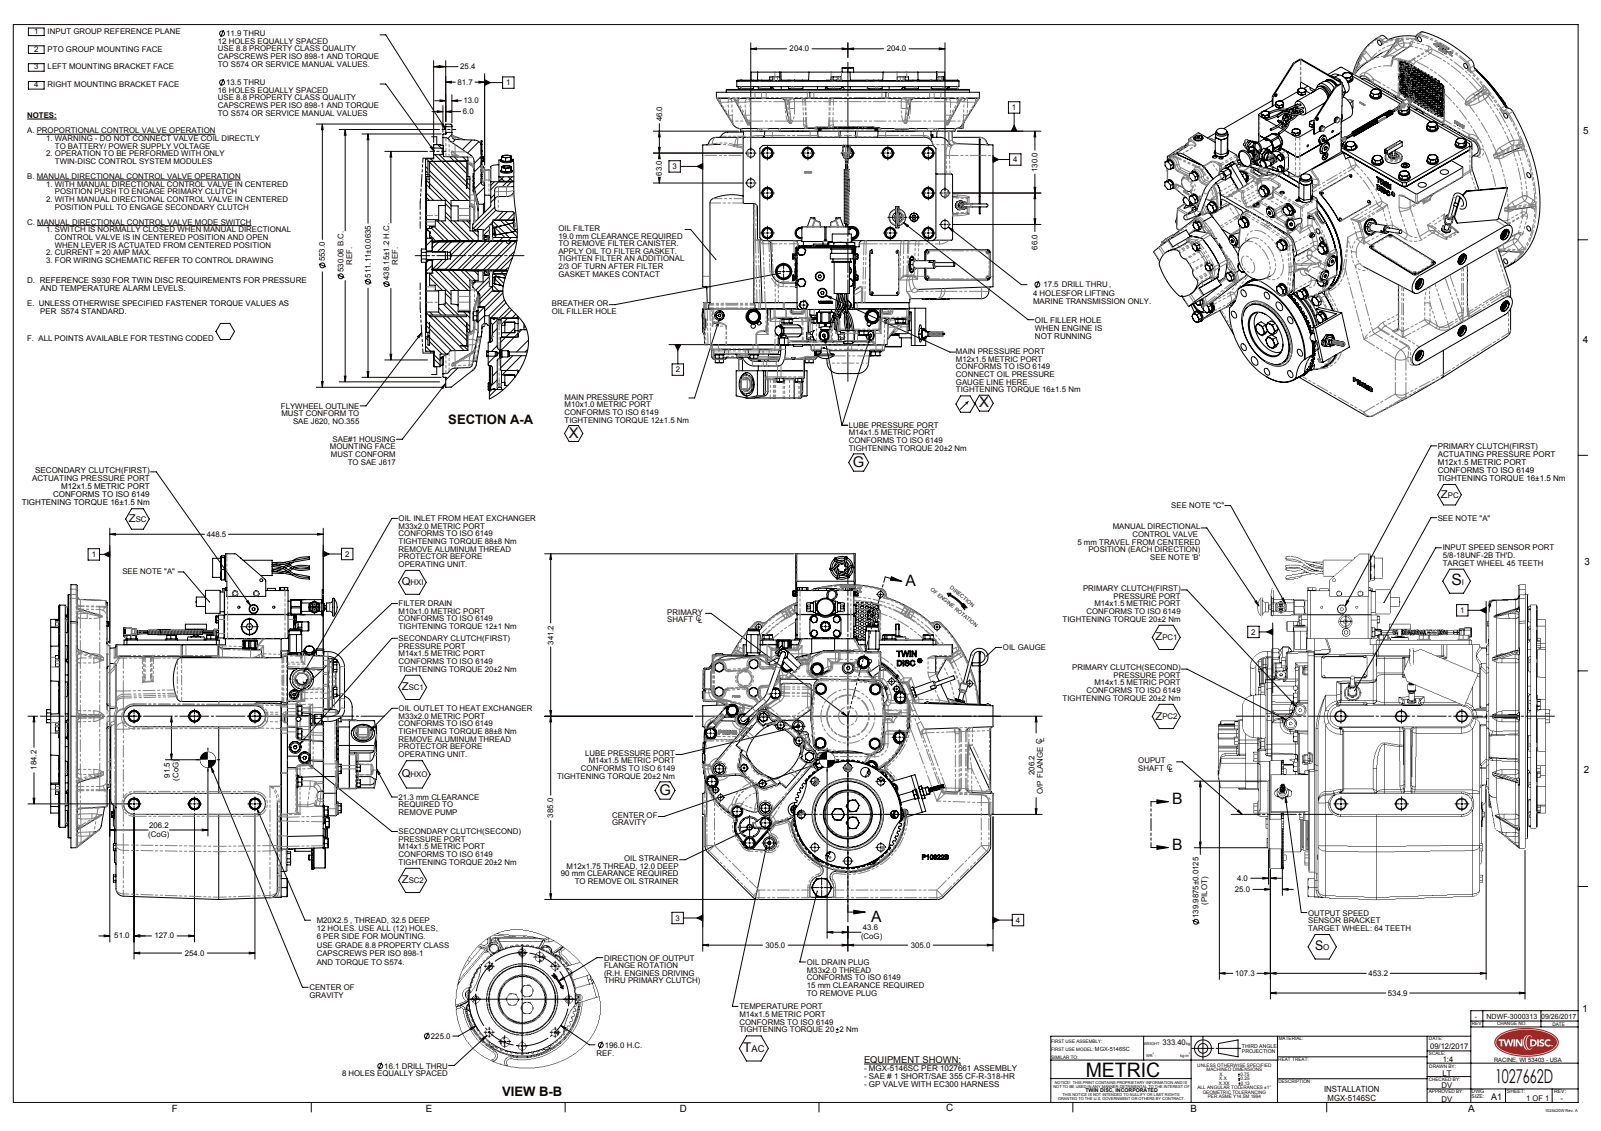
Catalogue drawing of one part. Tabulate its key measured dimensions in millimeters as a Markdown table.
| quantity | value |
| --- | --- |
| part name | 1027662D |
| STEP written by | SolidWorks 2015 (AUTOMOTIVE_DESIGN) |
| units | millimeters |
| bodies | 0 solids, 4531 faces (1640 planar, 1220 cylindrical, 1671 other) |
| overall size | 726.2 × 693.52 × 610.71 |
| round holes (diameter × count) | 7 × 94, 11.91 × 12, 25 × 10, 16.1 × 8, 20 × 6, 23.51 × 5, 9.33 × 4, 12 × 4, 17.5 × 4, 30 × 4, 10 × 3, 4.8 × 2 |
| round bosses / shafts (diameter × count) | 24 × 49, 18.9 × 9, 81 × 7, 10 × 6, 2.79 × 6, 19.85 × 5, 2.54 × 5, 16.8 × 4 |
| partial cylindrical surfaces (radius × count) | 2.5 × 89, 8 × 70, 6.5 × 61, 3 × 57, 39.71 × 54, 16 × 32, 3.5 × 23, 3.05 × 22 |
| main face-to-face distances | 0.39, 360.48, 360.09, 8, 365.66, 75, 13.48, 13.09, 347, 387.14 |
| hole center spacings | 10, 20.07, 20, 26.51, 459.05, 30, 34.68, 40 |
